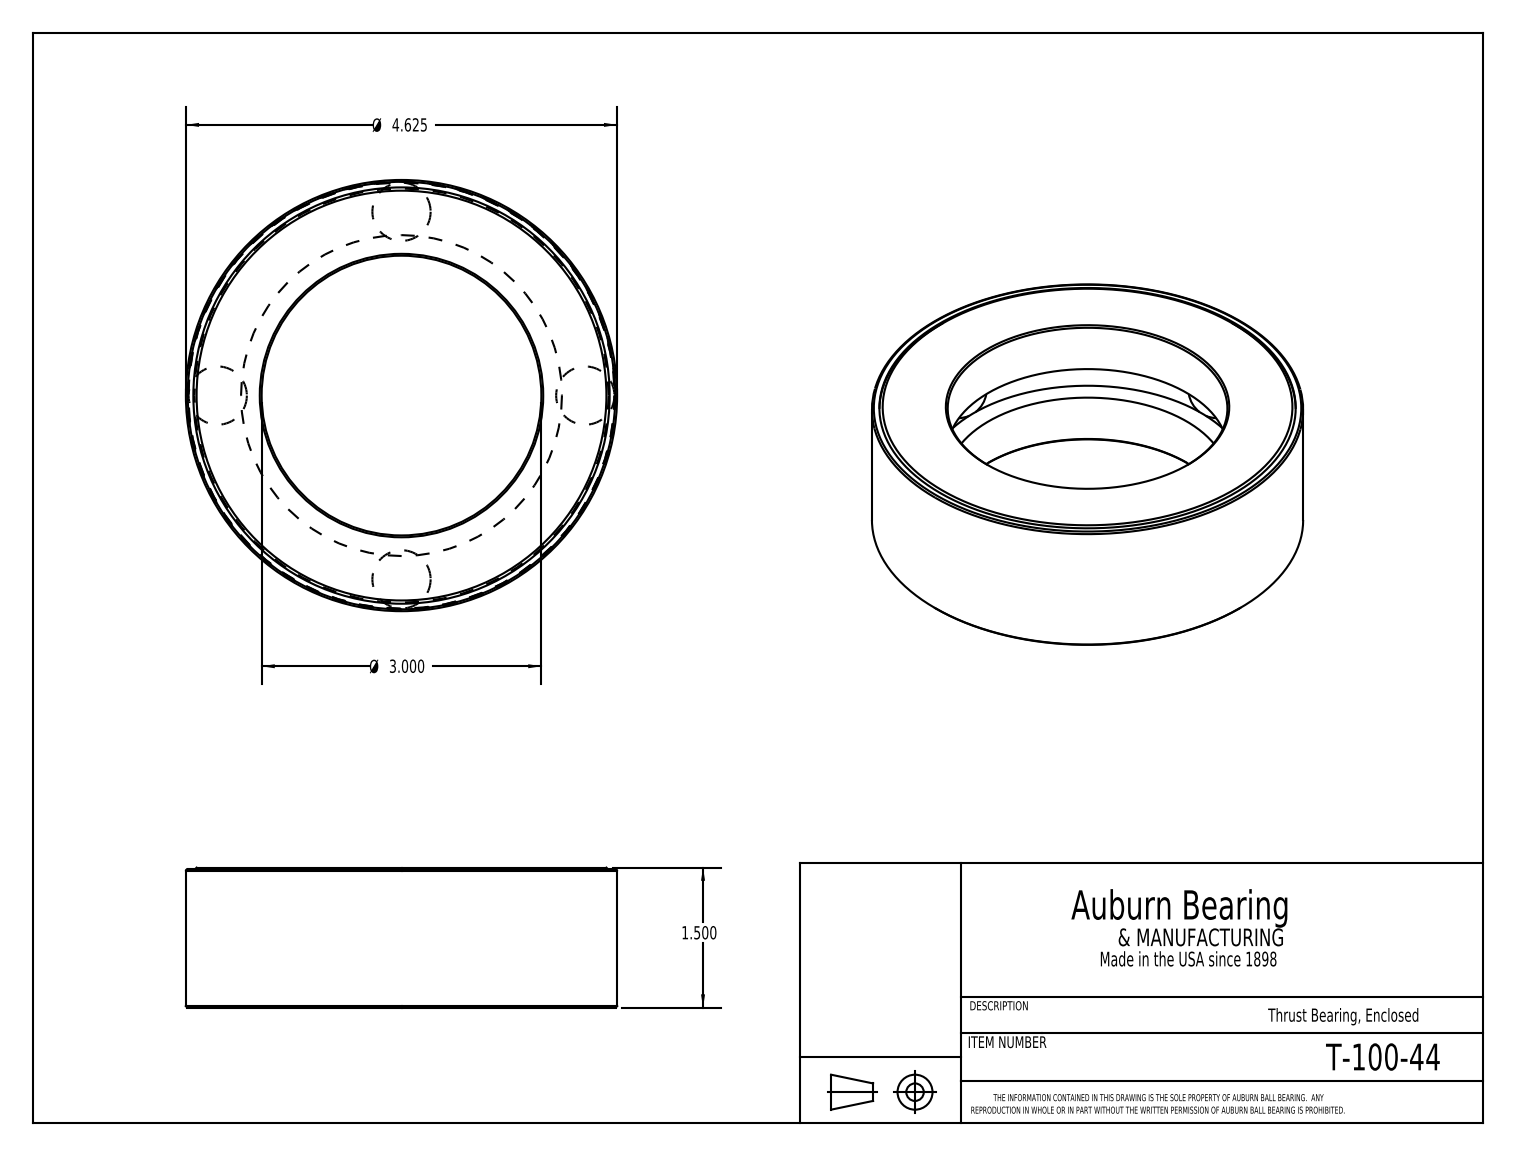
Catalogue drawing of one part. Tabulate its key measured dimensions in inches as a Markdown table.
| quantity | value |
| --- | --- |
| part name | T-100-44 |
| STEP written by | SolidWorks 2016 (CONFIG_CONTROL_DESIGN) |
| units | inches |
| bodies | 6 solids, 28 faces (9 planar, 7 cylindrical, 12 other) |
| overall size | 4.625 × 4.625 × 1.5 |
| volume | 10.38 in³ |
| surface area | 99.15 in² |
| round holes (diameter × count) | 3 × 1, 4.465 × 1, 4.585 × 1 |
| round bosses / shafts (diameter × count) | 4.625 × 1, 4.571 × 1 |
| main face-to-face distances | 1.5, 0.563, 0.937, 0.375, 1.485, 0.922, 0.548, 0.015, 1.465, 0.902 |
